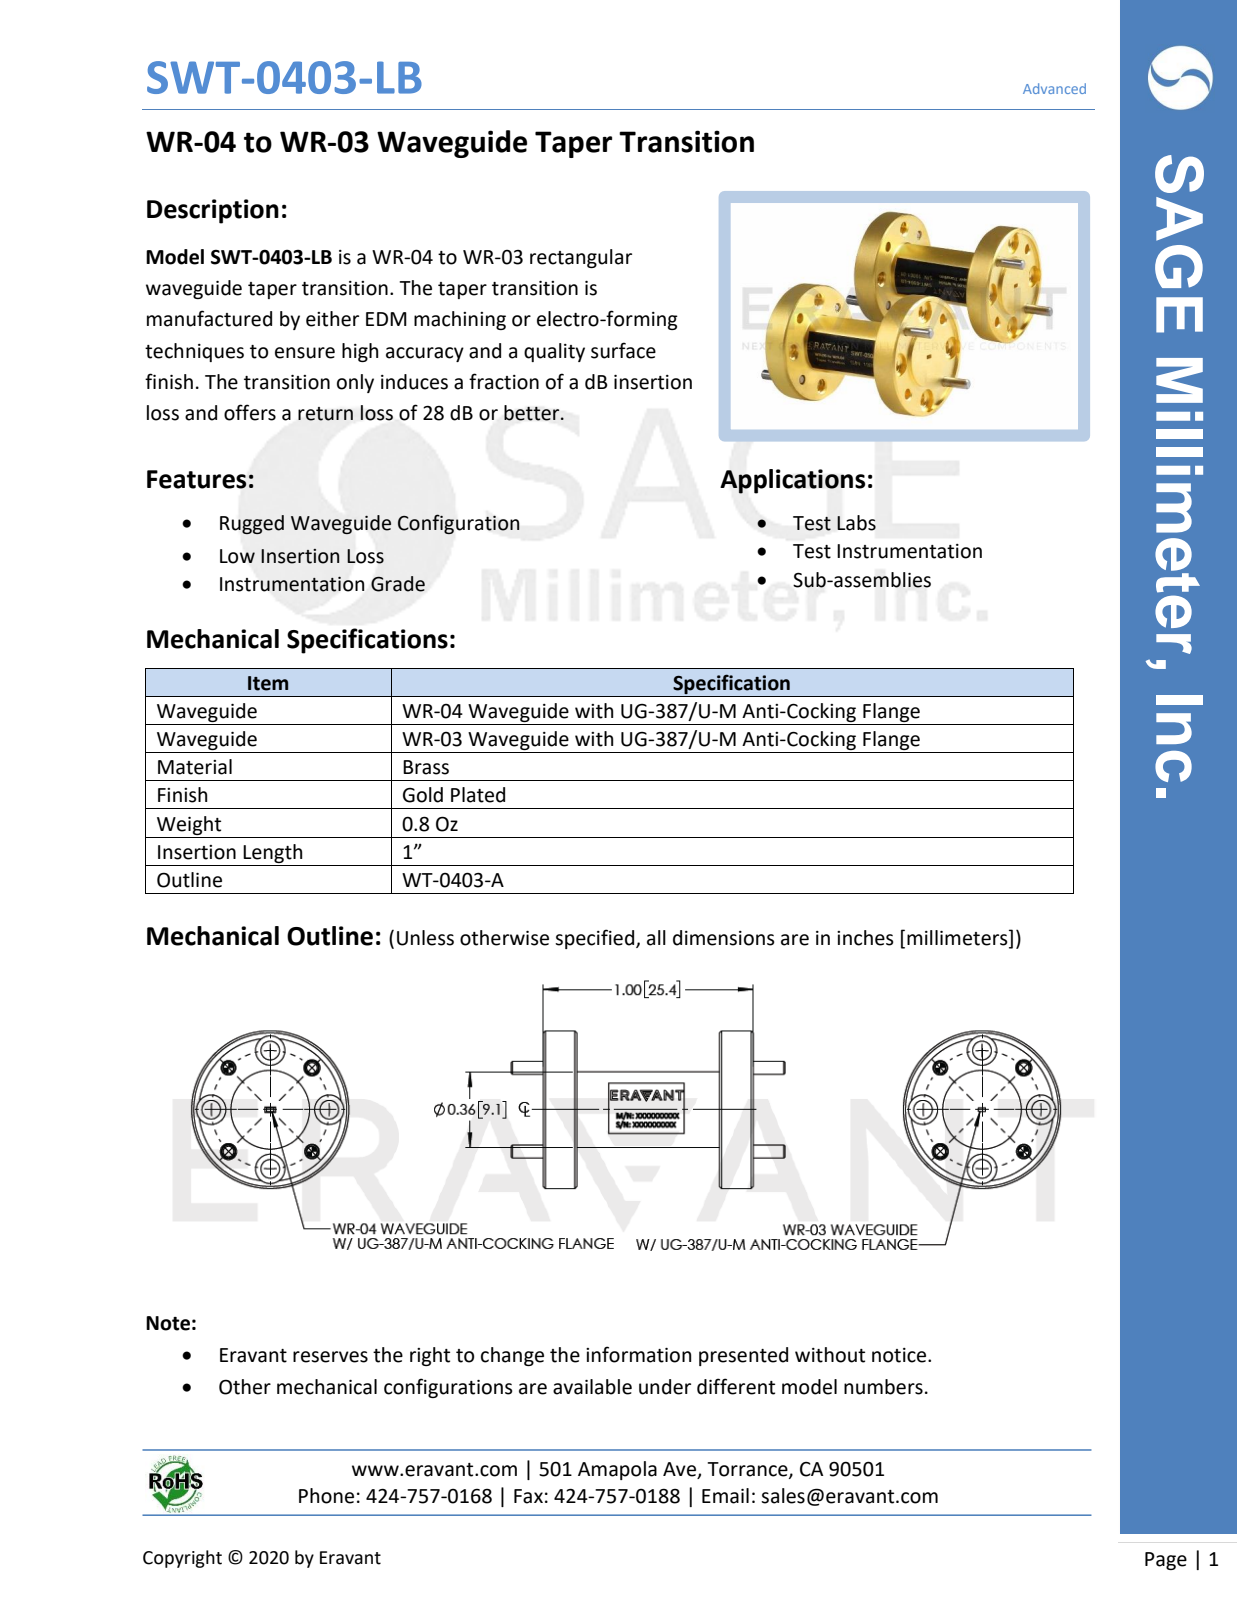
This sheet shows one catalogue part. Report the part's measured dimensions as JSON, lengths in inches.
{"part_name": "SWT-0403-LB", "step_written_by": "SolidWorks 2021 (CONFIG_CONTROL_DESIGN)", "units": "inches", "bodies": {"solids": 5, "faces": 148, "planar": 34, "cylindrical": 74, "other": 40}, "overall_size": [1.305, 0.75, 0.75], "volume_in3": 0.19, "surface_area_in2": 3.865, "round_holes": [[0.061, 4], [0.067, 4], [0.089, 4], [0.14, 4], [0.68, 1]], "round_bosses_or_shafts": [[0.063, 4], [0.75, 1], [0.375, 1], [0.36, 1]], "face_to_face_distances": [0.14, 0.82, 0.02, 0.16, 0.84, 0.98, 0.68, 0.96, 1, 0.06], "hole_center_spacings": [0.215, 0.281, 0.398, 0.519, 0.562]}
